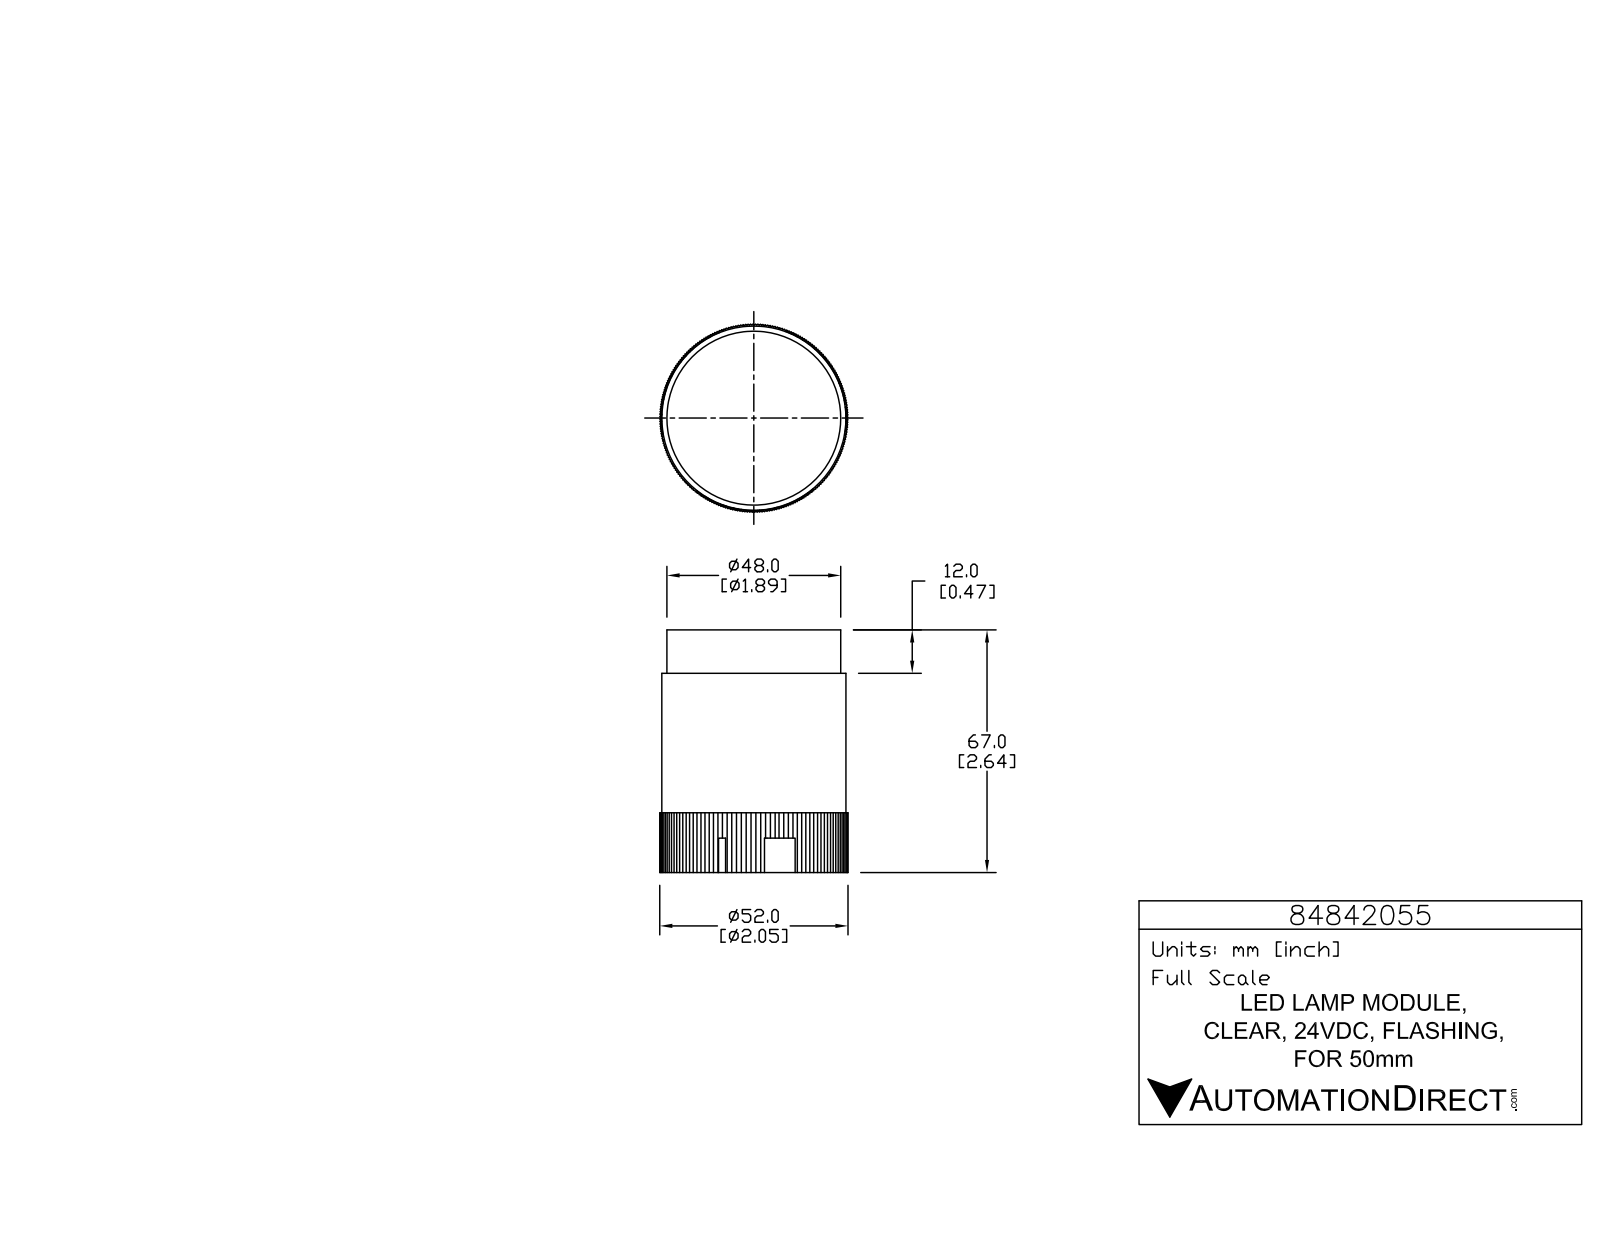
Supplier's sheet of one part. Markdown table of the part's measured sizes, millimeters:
| quantity | value |
| --- | --- |
| part name | 84842055 |
| STEP written by | SolidWorks 2015 (AUTOMOTIVE_DESIGN) |
| units | millimeters |
| bodies | 1 solid, 1265 faces (1020 planar, 245 cylindrical, 0 other) |
| overall size | 67 × 52 × 52 |
| volume | 112 600 mm³ |
| surface area | 17 820 mm² |
| round holes (diameter × count) | 1 × 3, 48.2 × 1 |
| round bosses / shafts (diameter × count) | 5.7 × 3, 1.4 × 3, 50.9 × 1, 48 × 1 |
| partial cylindrical surfaces (radius × count) | 0.2 × 6, 0.2 × 6, 0.2 × 6, 3.3 × 6, 0.1 × 3, 0.1 × 3, 0.2 × 3, 0.2 × 3 |
| main face-to-face distances | 55, 36.3, 36.3, 36.3, 12, 67, 36.3, 36.3, 43, 50.5 |
